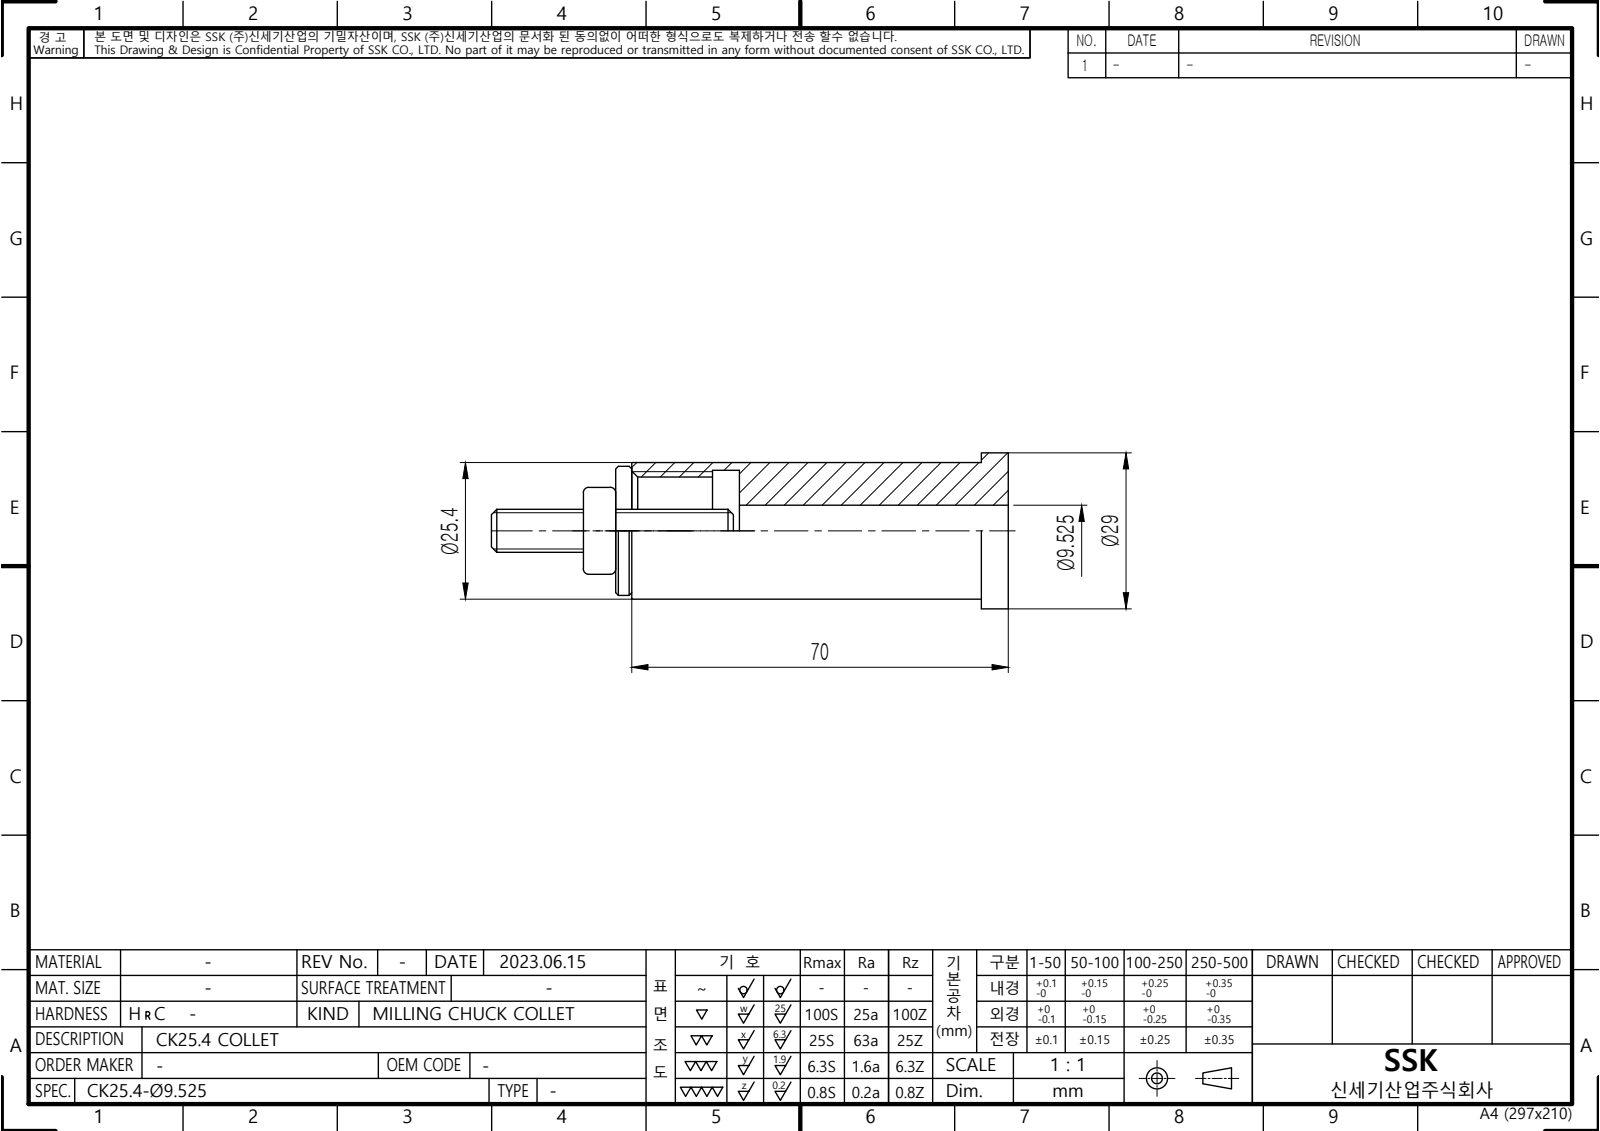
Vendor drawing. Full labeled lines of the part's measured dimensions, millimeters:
Part name (STEP PRODUCT): LO-CK19.05-9.525
STEP written by: Autodesk Inventor 2022 (AUTOMOTIVE_DESIGN)
Units: millimetres
Bodies: 1 solid, 10 faces (5 planar, 5 cylindrical, 0 other)
Overall size (bounding box): 70 × 29 × 29
Volume: 25 533 mm³ · Surface area: 9 764 mm²
Round holes (diameter × count): ⌀9.53 ×1, ⌀20.92 ×1, ⌀22.5 ×1
Round bosses / shafts (diameter × count): ⌀29 ×1, ⌀25.4 ×1
Main face-to-face distances: 50, 5, 20, 70, 65, 45, 15, 55
